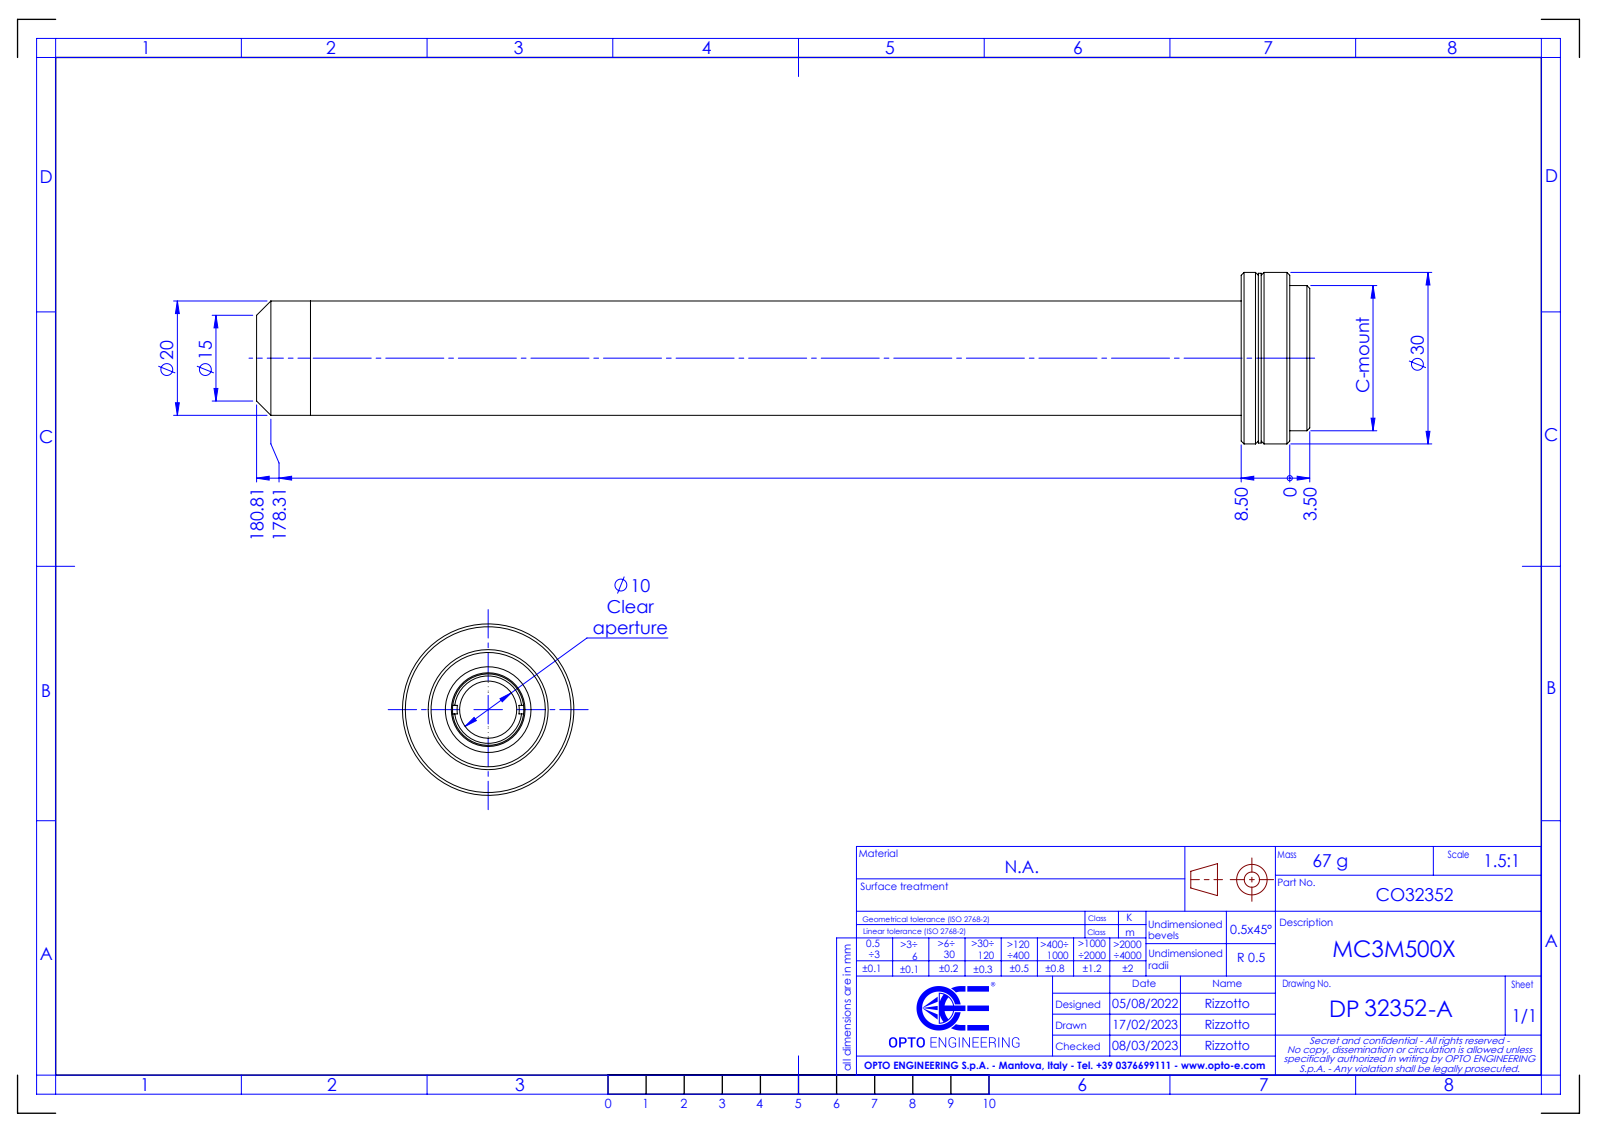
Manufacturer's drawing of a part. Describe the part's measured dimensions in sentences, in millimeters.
The part is named "DP32352-A_MC3M500X". Its 3-D file was written by "SolidWorks 2021 (CONFIG_CONTROL_DESIGN)". It is 0 solids with 64 faces: 16 planar, 22 cylindrical and 26 other. Overall it measures 184.31 by 30 by 30 millimeters. Round holes: 1 of diameter 10, 1 of diameter 12.5, 1 of diameter 17.5, 1 of diameter 18. Round bosses or shafts: 1 of diameter 30, 1 of diameter 29.7, 1 of diameter 25.4, 1 of diameter 20. The main face-to-face distances are 8.5, 3.5, 5, 3, 0.5, 5.5, 12, 9, 162.88, 165.88.
